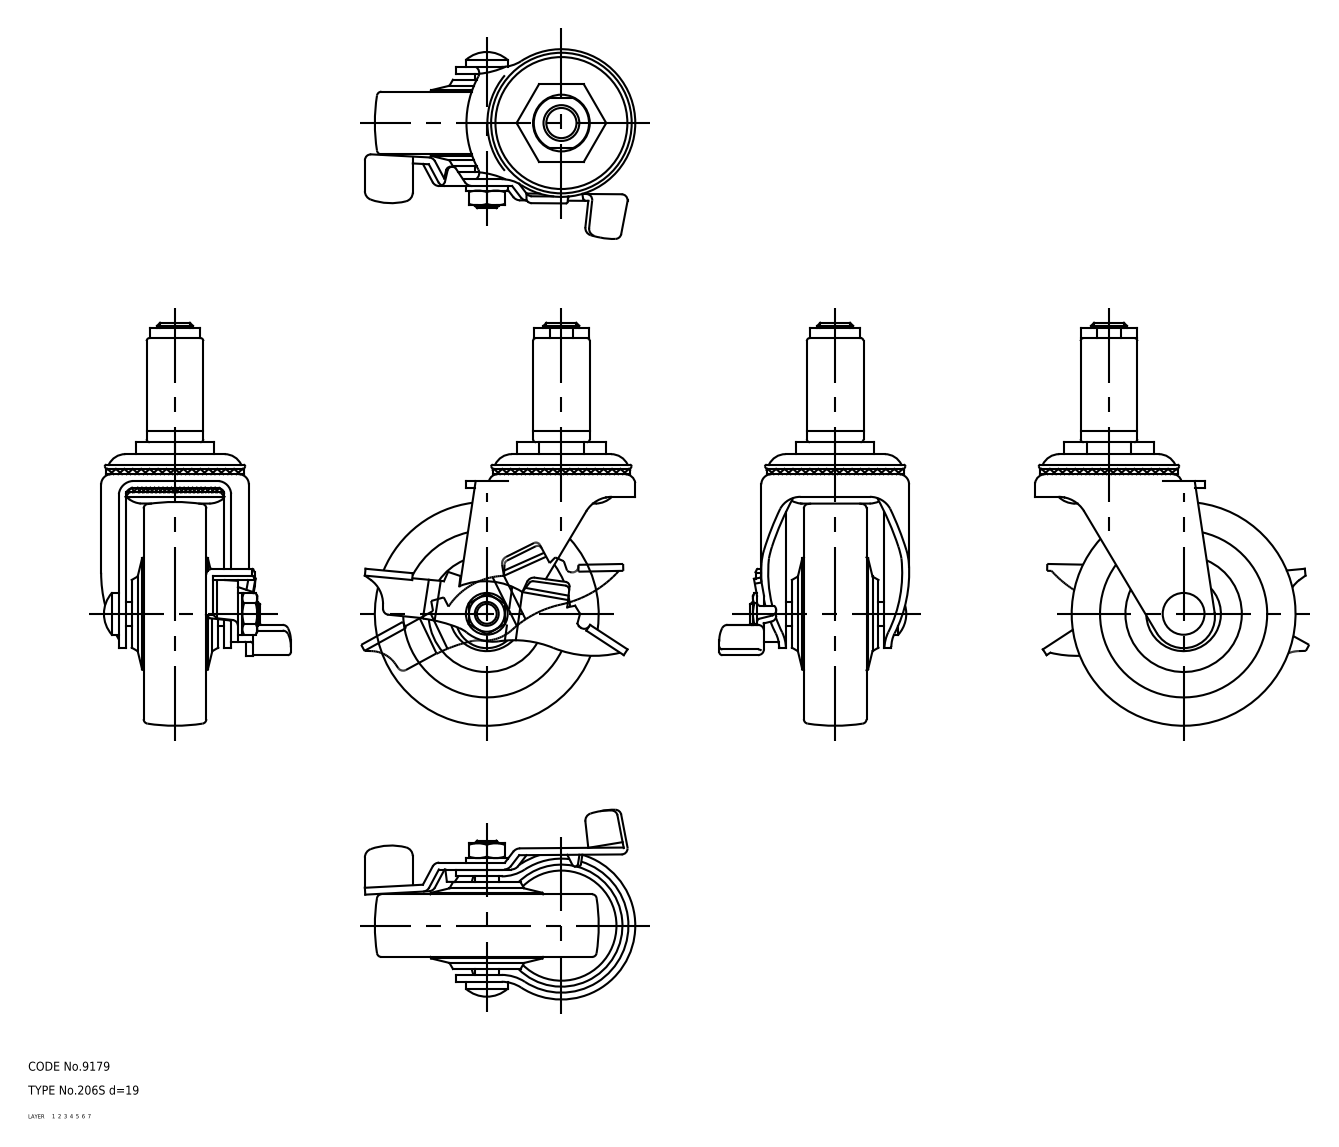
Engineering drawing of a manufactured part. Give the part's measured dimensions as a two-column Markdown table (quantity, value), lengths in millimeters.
| quantity | value |
| --- | --- |
| part name | wheel; main shaft; lever; axle (+1 more) |
| STEP written by | CADfix (AUTOMOTIVE_DESIGN) |
| units | millimeters |
| bodies | 5 solids, 277 faces (0 planar, 0 cylindrical, 277 other) |
| overall size | 135 × 90.59 × 63.57 |
| volume | 144 186 mm³ |
| surface area | 38 874 mm² |
